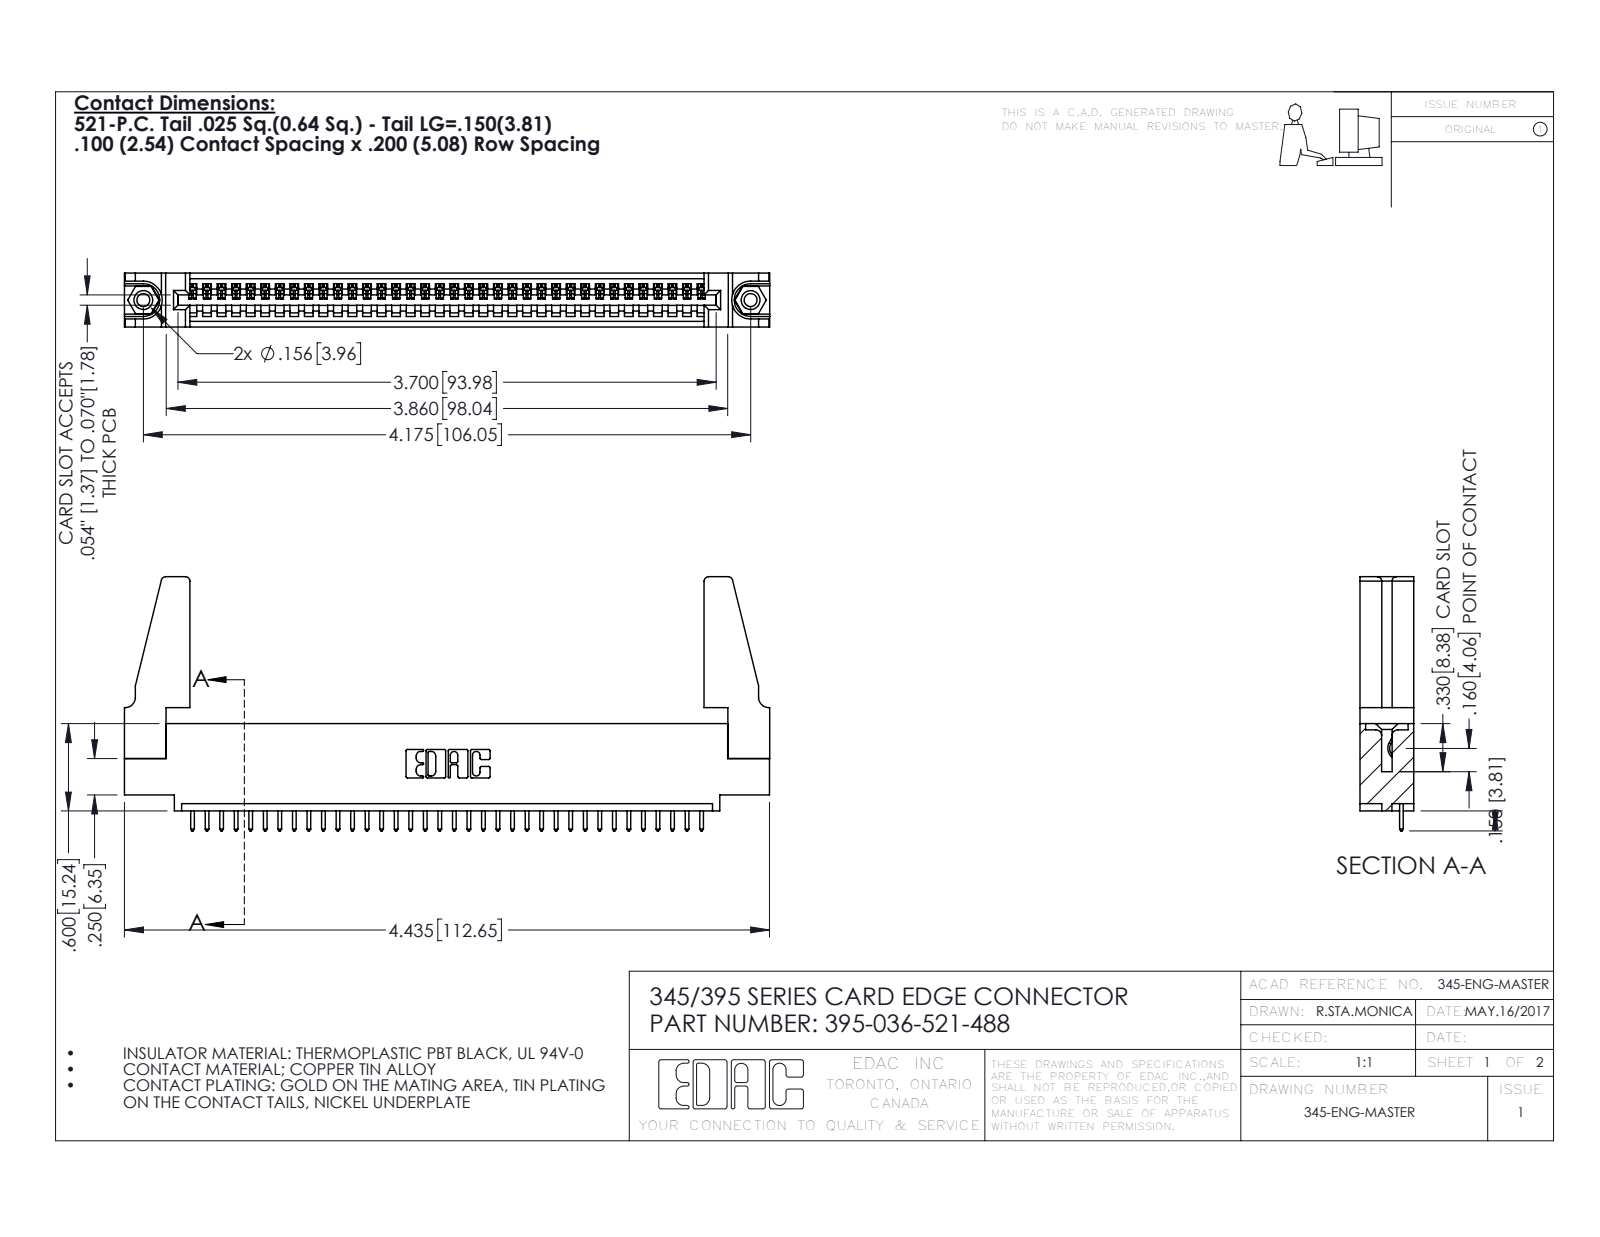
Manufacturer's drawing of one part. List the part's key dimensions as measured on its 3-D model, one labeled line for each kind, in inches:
Part name (STEP PRODUCT): 395-036-521-488; 345-220-078_345-220-088; 345 Part_0.110 Offset - 0.156 Dia-TH; 345-250-001_345-250-001-102 (+1 more)
STEP written by: SolidWorks 2016 (CONFIG_CONTROL_DESIGN)
Units: inches
Bodies: 41 solids, 2342 faces (1596 planar, 730 cylindrical, 16 other)
Overall size (bounding box): 4.436 × 1.747 × 0.37
Volume: 0.838 in³ · Surface area: 25.81 in²
Round holes (diameter × count): ⌀0.089 ×2, ⌀0.125 ×2, ⌀0.156 ×2, ⌀0.064 ×1
Round bosses / shafts (diameter × count): ⌀0.155 ×2
Partial cylindrical surfaces — rounded edges, fillets, slot ends (radius × count): R0.006 ×72, R0.01 ×72, R0.01 ×22, R0.03 ×8, R0.007 ×6, R0.031 ×6, R0.026 ×3, R0.031 ×2
Main face-to-face distances: 0.072, 0.298, 0.37, 0.2, 0.098, 0.272, 0.025, 0.225, 0.149, 0.072
Hole centre spacings: 0.27, 3.939, 4.175
